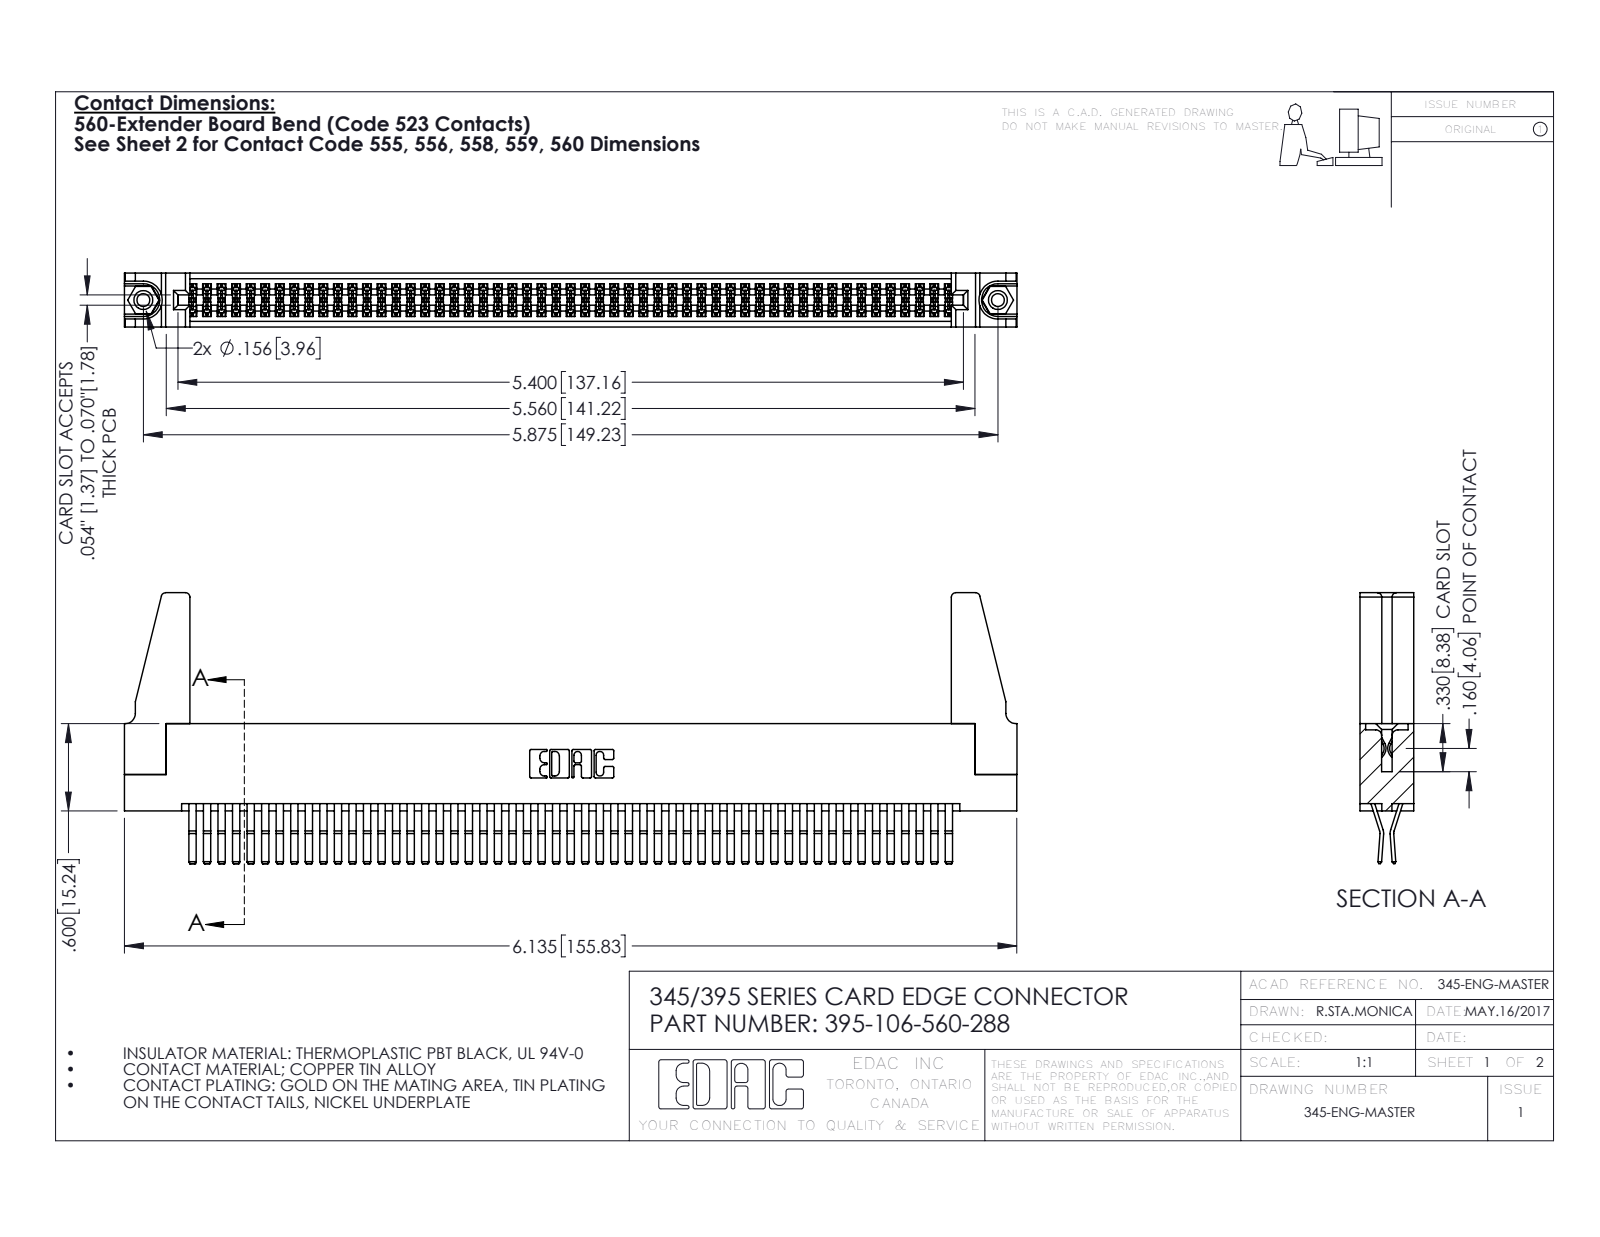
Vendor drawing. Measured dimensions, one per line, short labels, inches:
name: 345-220-078_345-220-088; 395-106-560-288; 345-292-001_560 Tail; 345-250-001_345-250-001-102 (+1 more)
written by: SolidWorks 2016 (CONFIG_CONTROL_DESIGN)
unit: in
bodies: 111 solids, 5762 faces (3650 planar, 2096 cylindrical, 16 other)
size: 6.136 × 1.862 × 0.37
volume: 1.171 in³; area: 44.45 in²
holes: 2× ⌀0.089, 2× ⌀0.125, 2× ⌀0.156, 1× ⌀0.064
bosses: 2× ⌀0.155
rounds: 160× R0.006, 22× R0.01, 8× R0.03, 6× R0.007, 6× R0.031, 3× R0.026, 2× R0.01, 2× R0.014
face distances: 0.072, 0.298, 0.025, 0.37, 0.2, 0.098, 0.272, 0.225, 0.175, 0.149
hole spacings: 0.27, 5.639, 5.875
